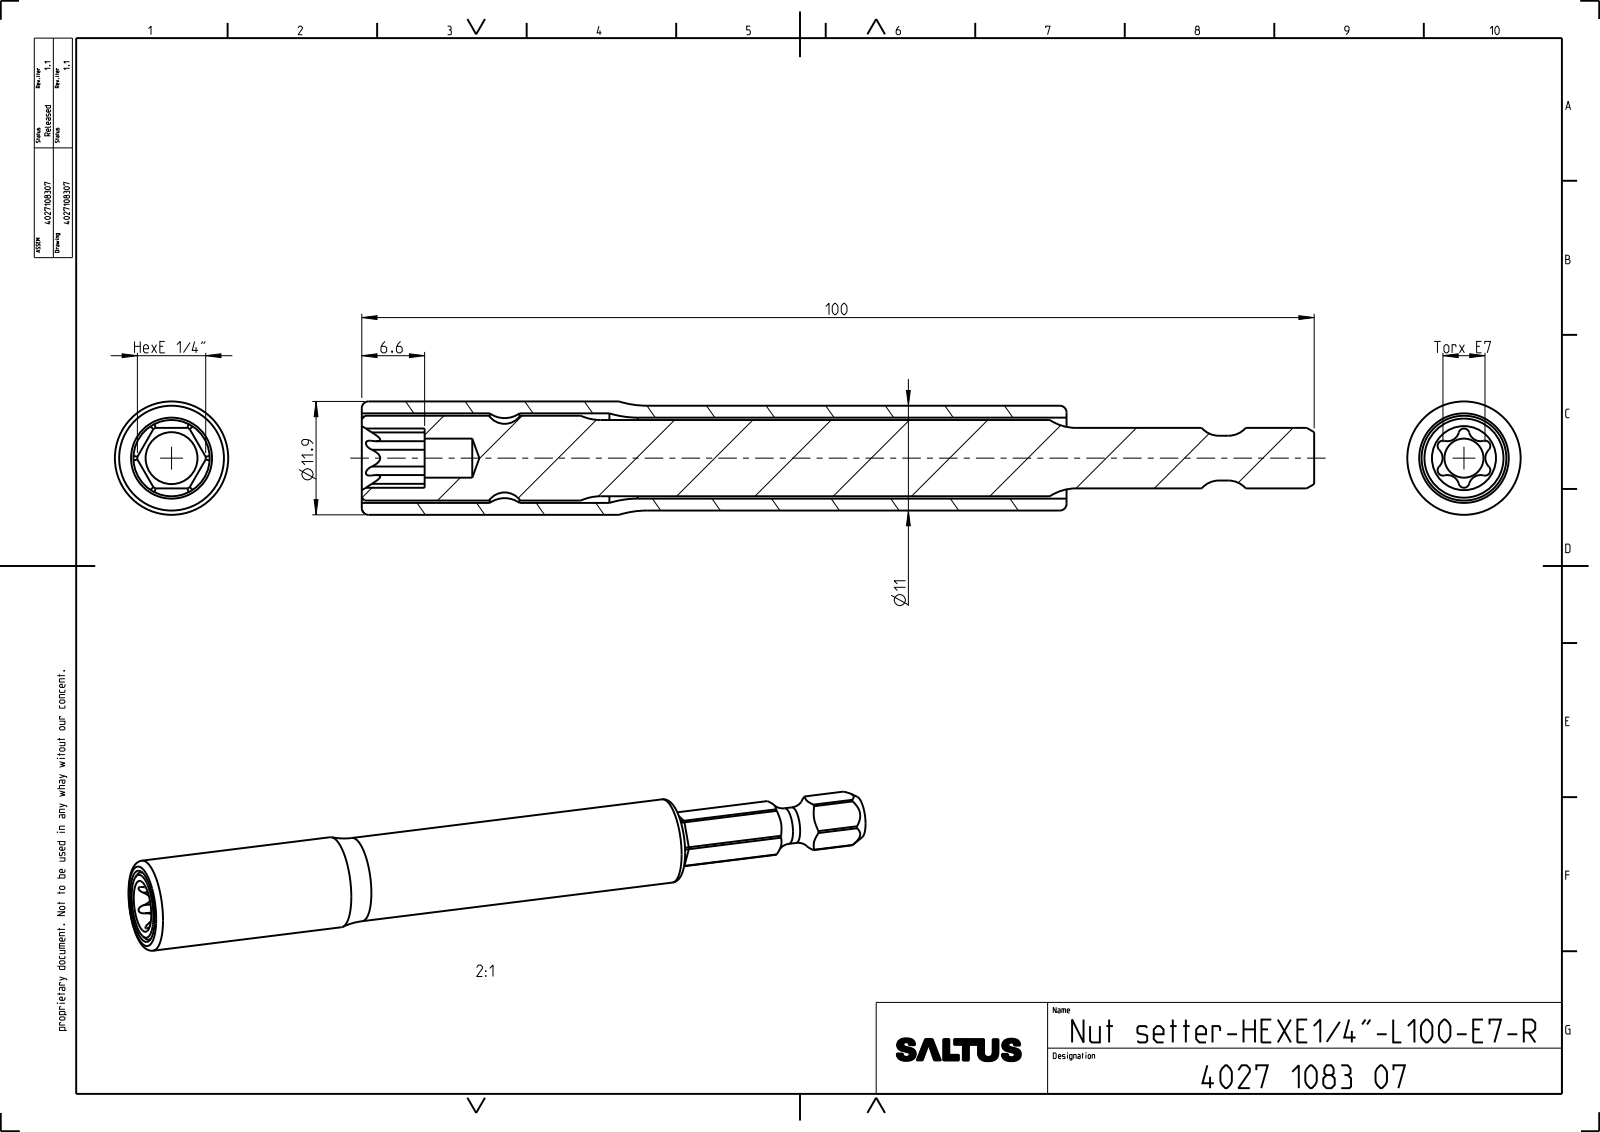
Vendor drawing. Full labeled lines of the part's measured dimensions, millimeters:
Part name (STEP PRODUCT): 4027911277; 4027044595; 4027108307_ASM
STEP written by: CREO PARAMETRIC BY PTC INC, 2022414 (CONFIG_CONTROL_DESIGN)
Units: millimetres
Bodies: 2 solids, 99 faces (17 planar, 50 cylindrical, 32 other)
Overall size (bounding box): 100 × 11.9 × 11.9
Volume: 7 517 mm³ · Surface area: 7 501 mm²
Round holes (diameter × count): ⌀4.1 ×1, ⌀8.5 ×1, ⌀9.4 ×1
Round bosses / shafts (diameter × count): ⌀11.9 ×1, ⌀11 ×1, ⌀8.9 ×1, ⌀8 ×1, ⌀4.7 ×1
Partial cylindrical surfaces — rounded edges, fillets, slot ends (radius × count): R0.56 ×6, R1.25 ×6, R5 ×6, R3.59 ×1
Main face-to-face distances: 6.34, 6.36, 100, 26, 74, 93.4, 67.4, 6.6
